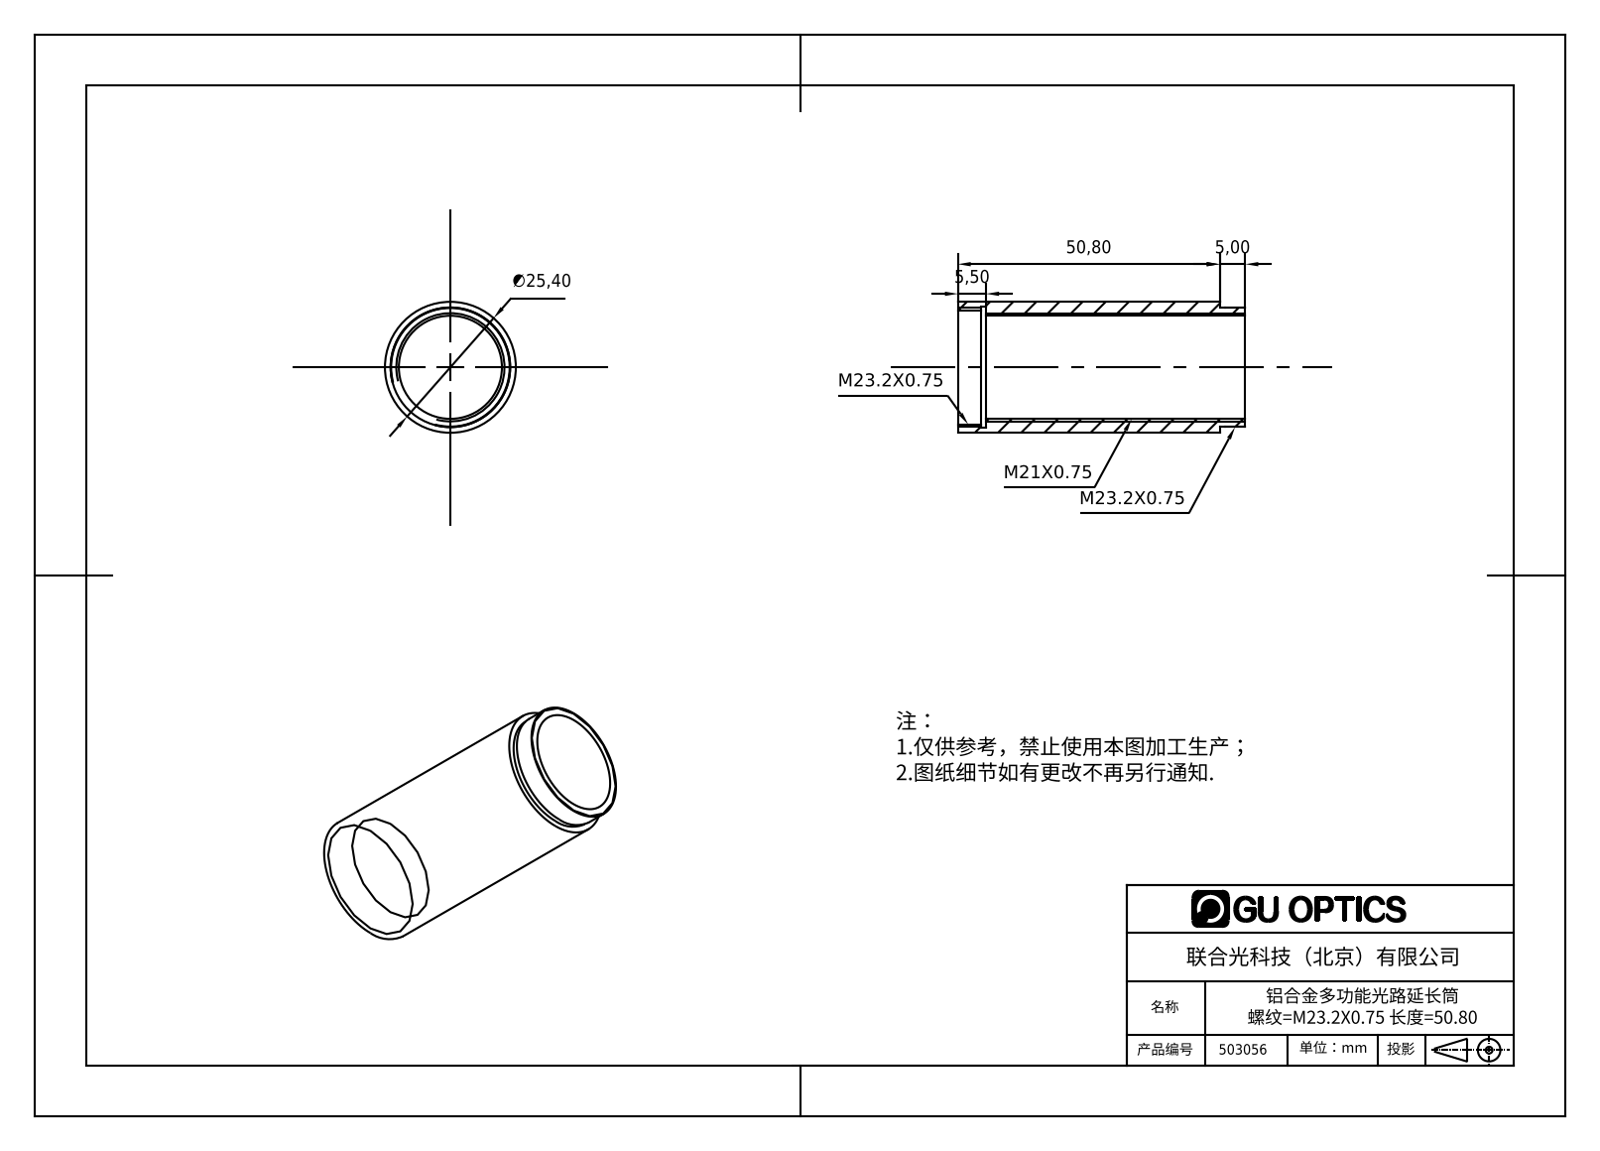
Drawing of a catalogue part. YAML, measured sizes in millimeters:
part_name: "503056"
step_written_by: "SolidWorks 2016 (AUTOMOTIVE_DESIGN)"
units: millimeters
bodies: {solids: 1, faces: 18, planar: 6, cylindrical: 12, other: 0}
overall_size: [55.8, 25.4, 25.4]
volume: 9873
surface_area: 8451
round_holes:
  - {diameter: 20, count: 1}
  - {diameter: 22.2, count: 1}
  - {diameter: 23.4, count: 1}
round_bosses_or_shafts:
  - {diameter: 25.4, count: 1}
  - {diameter: 23.2, count: 1}
  - {diameter: 23, count: 1}
face_to_face_distances: [5.5, 55.8, 50.3, 50.8, 45.3, 5, 1, 46.3, 4.5, 51.3]
